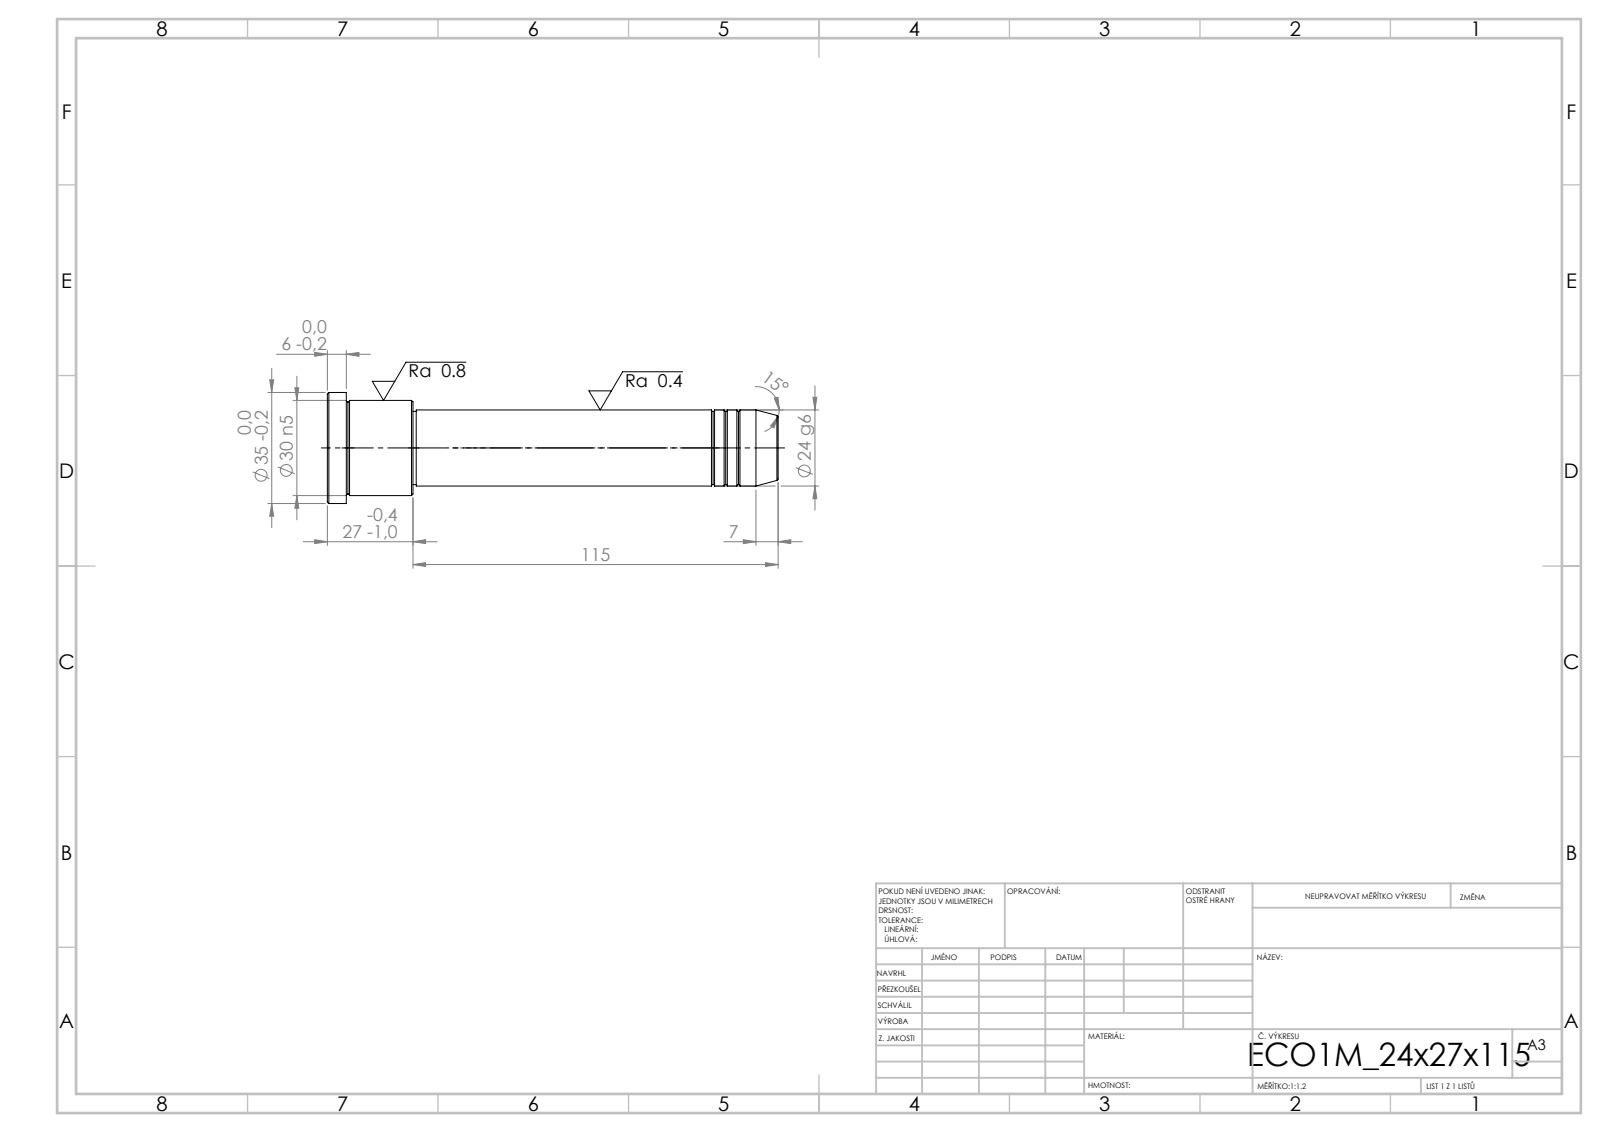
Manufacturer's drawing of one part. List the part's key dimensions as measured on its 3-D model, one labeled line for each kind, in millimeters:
STEP written by: SolidWorks 2019 (CONFIG_CONTROL_DESIGN)
Units: millimetres
Bodies: 1 solid, 43 faces (5 planar, 14 cylindrical, 24 other)
Overall size (bounding box): 142 × 35 × 35
Volume: 71 985 mm³ · Surface area: 13 253 mm²
Round bosses / shafts (diameter × count): ⌀35 ×1, ⌀30 ×1, ⌀24 ×1, ⌀23 ×1
Main face-to-face distances: 142, 136, 6, 115, 21, 27, 114, 1, 22, 28
